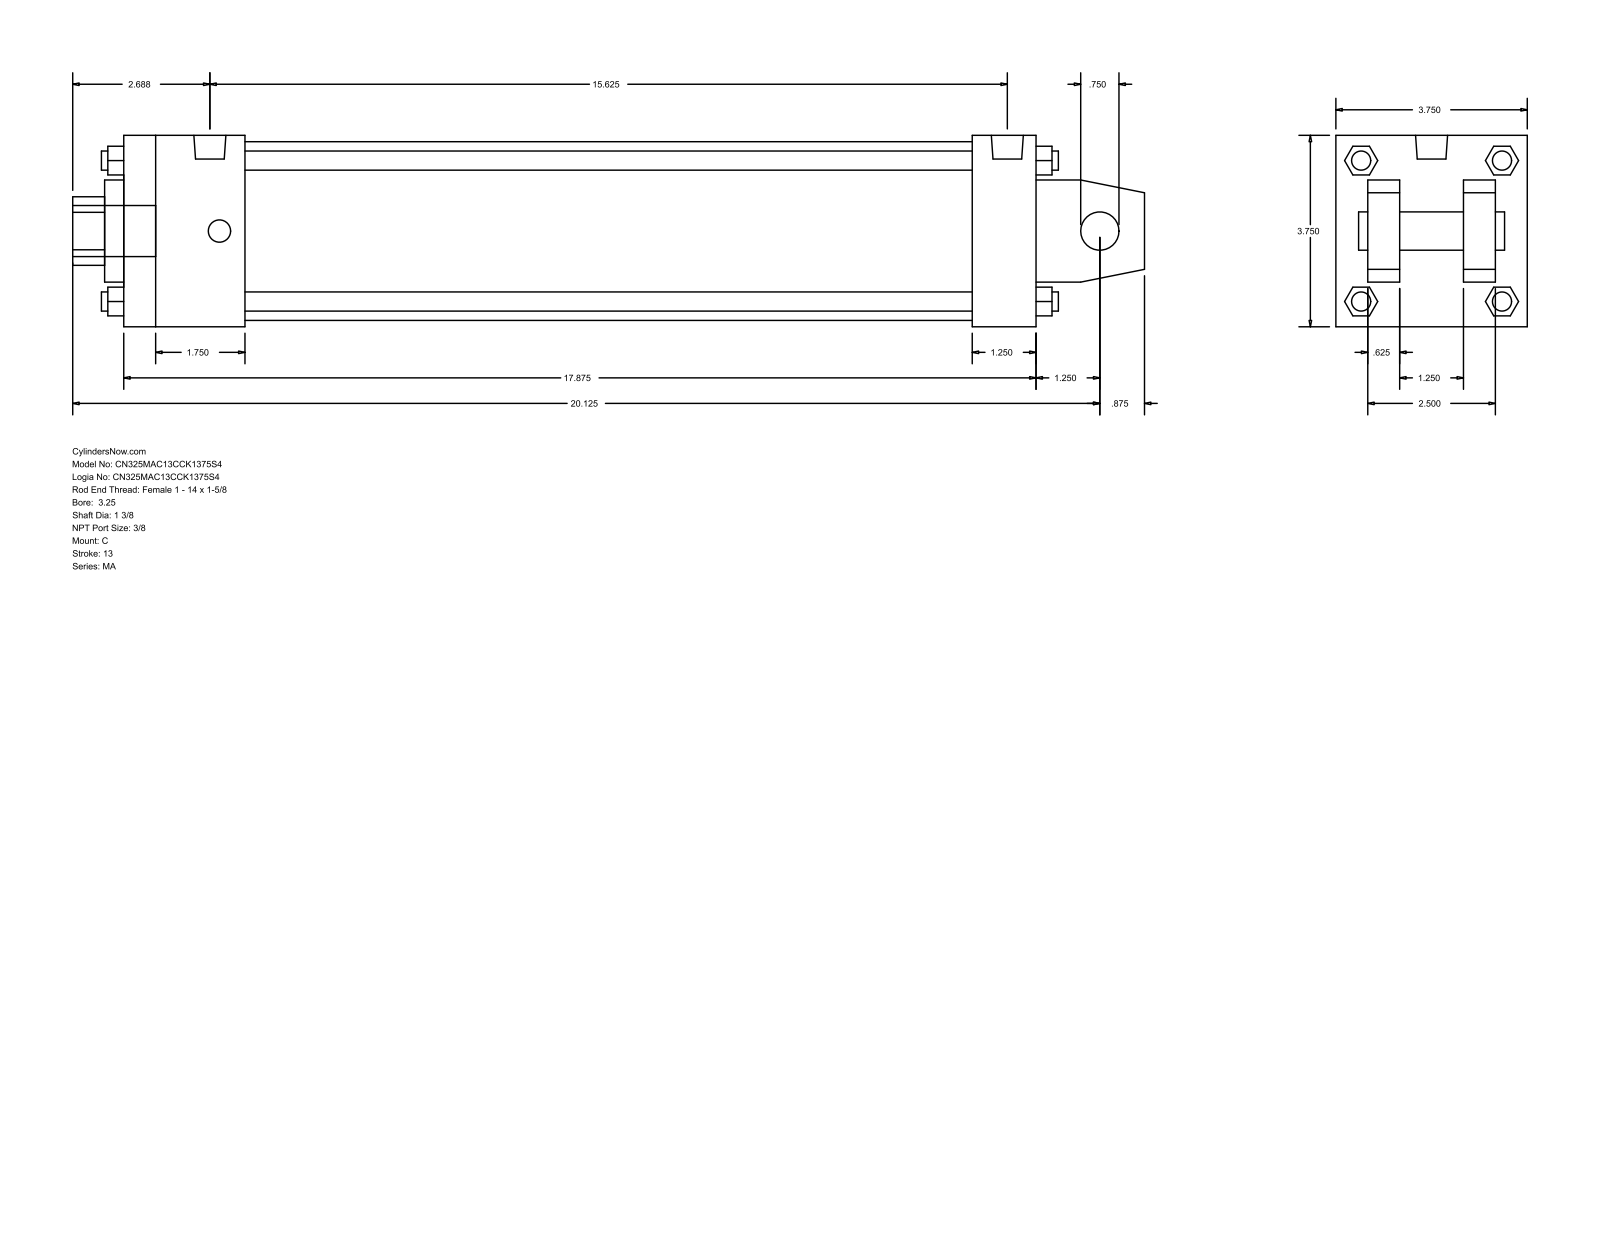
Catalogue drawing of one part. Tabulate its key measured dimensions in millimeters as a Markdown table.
| quantity | value |
| --- | --- |
| part name | MA_C__0325_1.375 |
| STEP written by | GSSL Pune (CONFIG_CONTROL_DESIGN) |
| units | millimeters |
| bodies | 0 solids, 139 faces (108 planar, 31 cylindrical, 0 other) |
| overall size | 533.4 × 95.25 × 95.25 |
| round holes (diameter × count) | 19.05 × 1, 34.92 × 1, 50.8 × 1, 88.9 × 1 |
| round bosses / shafts (diameter × count) | 11.11 × 4, 9.53 × 4, 15.93 × 2, 25.4 × 1 |
| partial cylindrical surfaces (radius × count) | 17.06 × 1 |
| main face-to-face distances | 95.24, 15.87, 63.5, 454.03, 31.74, 79.37, 47.63, 422.28, 31.75, 60.32 |
